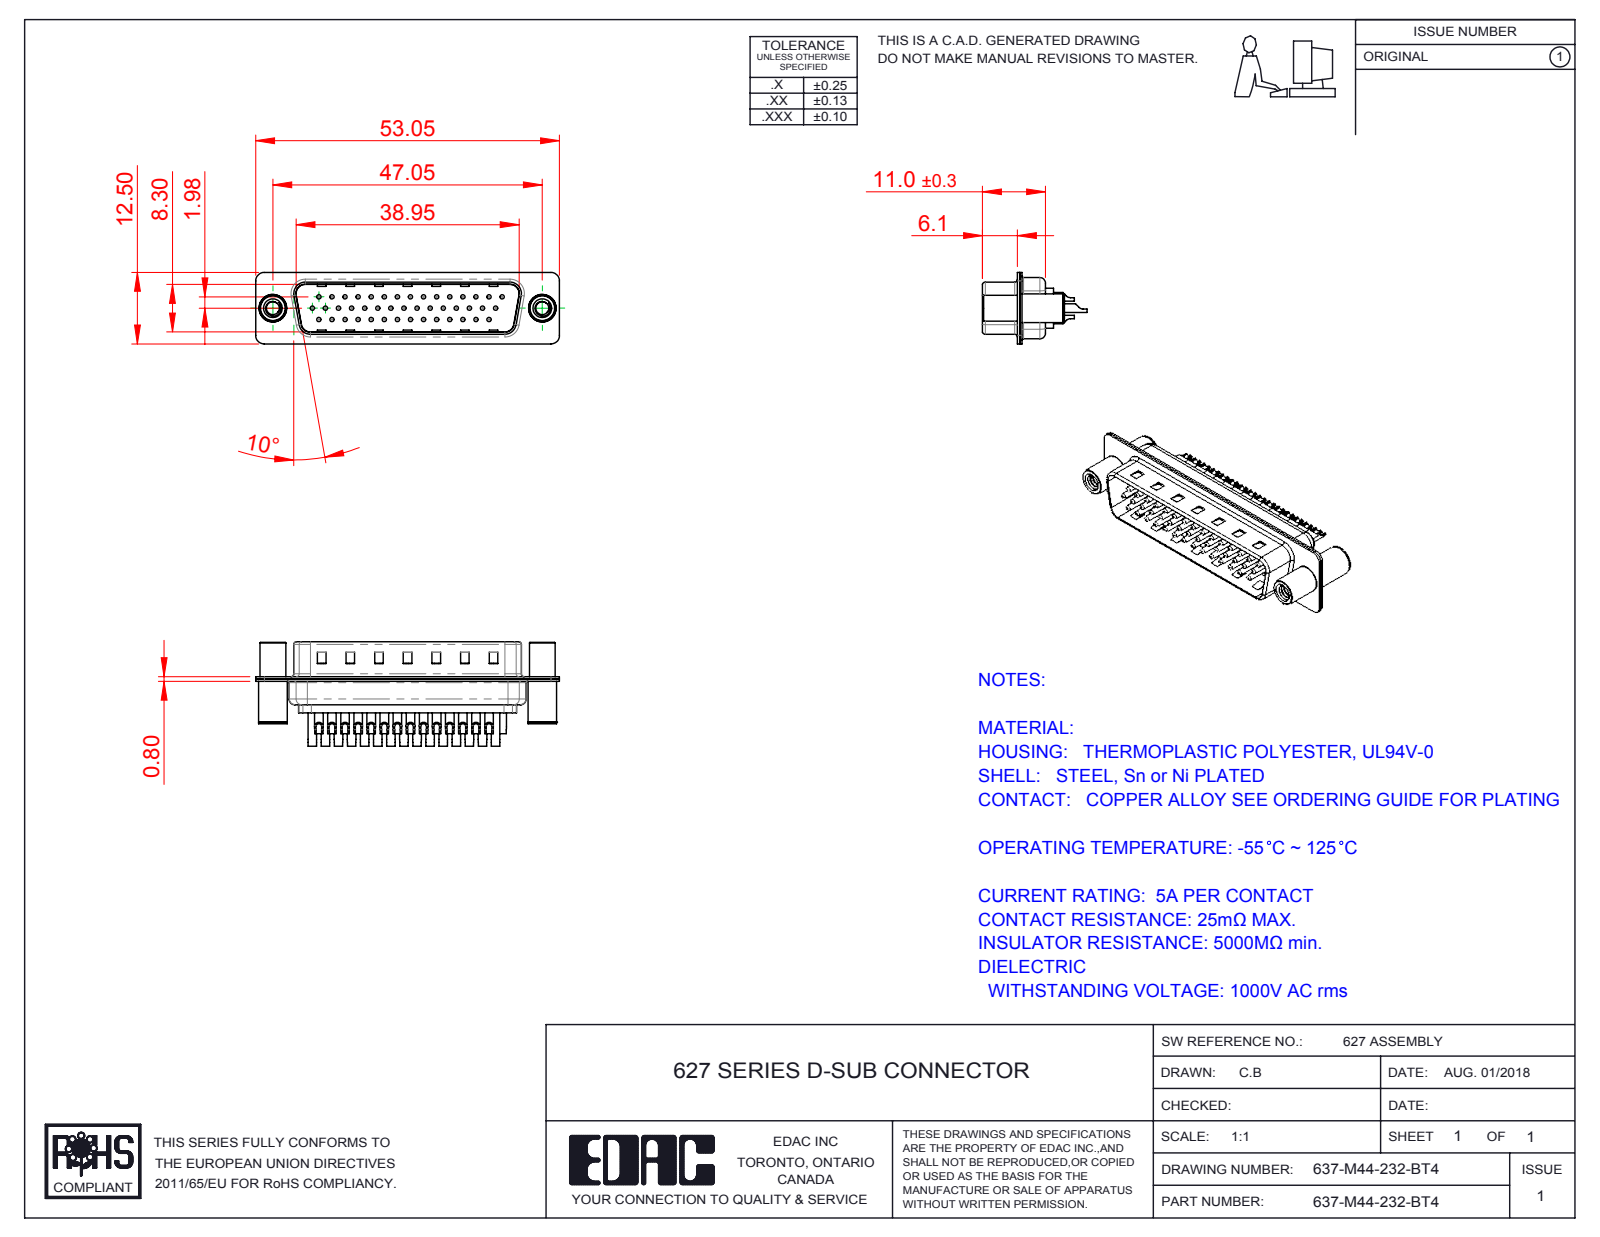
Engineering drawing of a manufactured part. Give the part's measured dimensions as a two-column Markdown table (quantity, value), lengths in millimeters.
| quantity | value |
| --- | --- |
| part name | 637M Housing_44 Contacts; 637M Shell Front_44 Contacts; 637M Contact Row 1_32; 637M Contact Row 3_32 (+4 more) |
| STEP written by | SolidWorks 2016 (CONFIG_CONTROL_DESIGN) |
| units | millimeters |
| bodies | 49 solids, 2090 faces (573 planar, 893 cylindrical, 624 other) |
| overall size | 53.05 × 18.25 × 12.5 |
| volume | 3 261 mm³ |
| surface area | 9 539 mm² |
| round holes (diameter × count) | 0.75 × 44, 1 × 44, 1.6 × 44, 2 × 44, 2.26 × 2, 3.26 × 2, 4 × 2, 4.8 × 2 |
| round bosses / shafts (diameter × count) | 1.5 × 44, 2 × 3, 0.75 × 3, 5 × 2, 4.9 × 2, 4.5 × 2 |
| partial cylindrical surfaces (radius × count) | 1.5 × 16, 2 × 12, 0.5 × 8, 1.6 × 8, 1 × 7, 0.25 × 4, 0.6 × 4, 0.65 × 4 |
| main face-to-face distances | 0.4, 0.8, 9.5, 9.1, 8.7, 9.9, 0.75, 0.35, 1.1, 1.2 |
| hole center spacings | 2.28, 3.96, 2.29, 4.57, 8.24, 6.86, 11.43, 14.99 |
